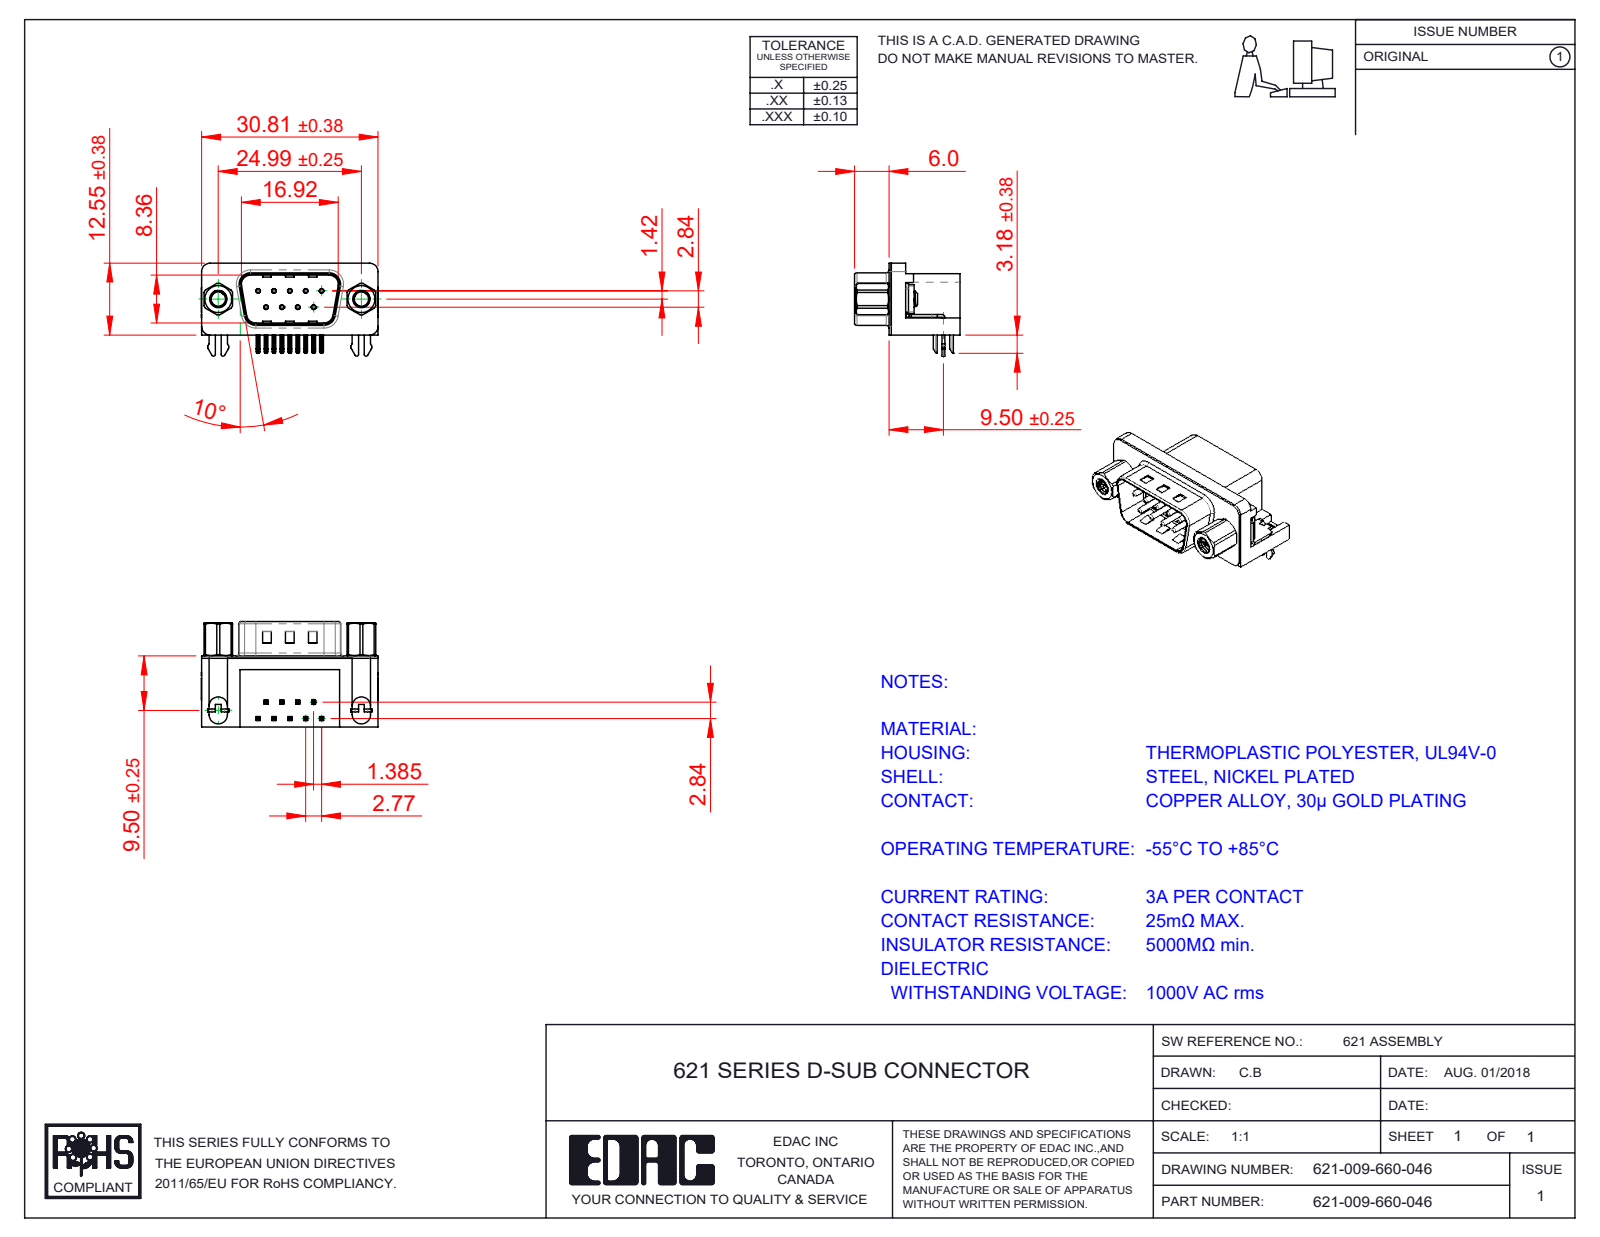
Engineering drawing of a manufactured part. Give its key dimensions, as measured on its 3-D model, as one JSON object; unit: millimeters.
{"part_name": "621 4 Prong Board Lock; 621 M3 Hex Standoff 5; 621 M3 Threaded Rivet; 621-009-660-046 (+4 more)", "step_written_by": "SolidWorks 2016 (CONFIG_CONTROL_DESIGN)", "units": "millimeters", "bodies": {"solids": 17, "faces": 1259, "planar": 637, "cylindrical": 417, "other": 205}, "overall_size": [30.89, 18.4, 16.25], "volume_mm3": 3495, "surface_area_mm2": 5028, "round_holes": [[0.35, 9], [0.8, 9], [2, 2], [2.5, 2], [4, 2], [4.8, 2], [5, 2]], "round_bosses_or_shafts": [[0.75, 9], [3, 4], [4.9, 2], [4.75, 2], [3.9, 2]], "partial_cylinders_radius": [[0.25, 48], [0.12, 18], [1, 16], [0.5, 9], [1.5, 8], [1.6, 8], [0.9, 4], [2, 4]], "face_to_face_distances": [0.4, 12, 12.4, 10.35, 9.5, 2.5, 2.9, 2.1, 0.35, 10.7], "hole_center_spacings": [3.16, 2.77, 5.54, 5.03, 5.04, 8.31, 7.48, 7.49]}
